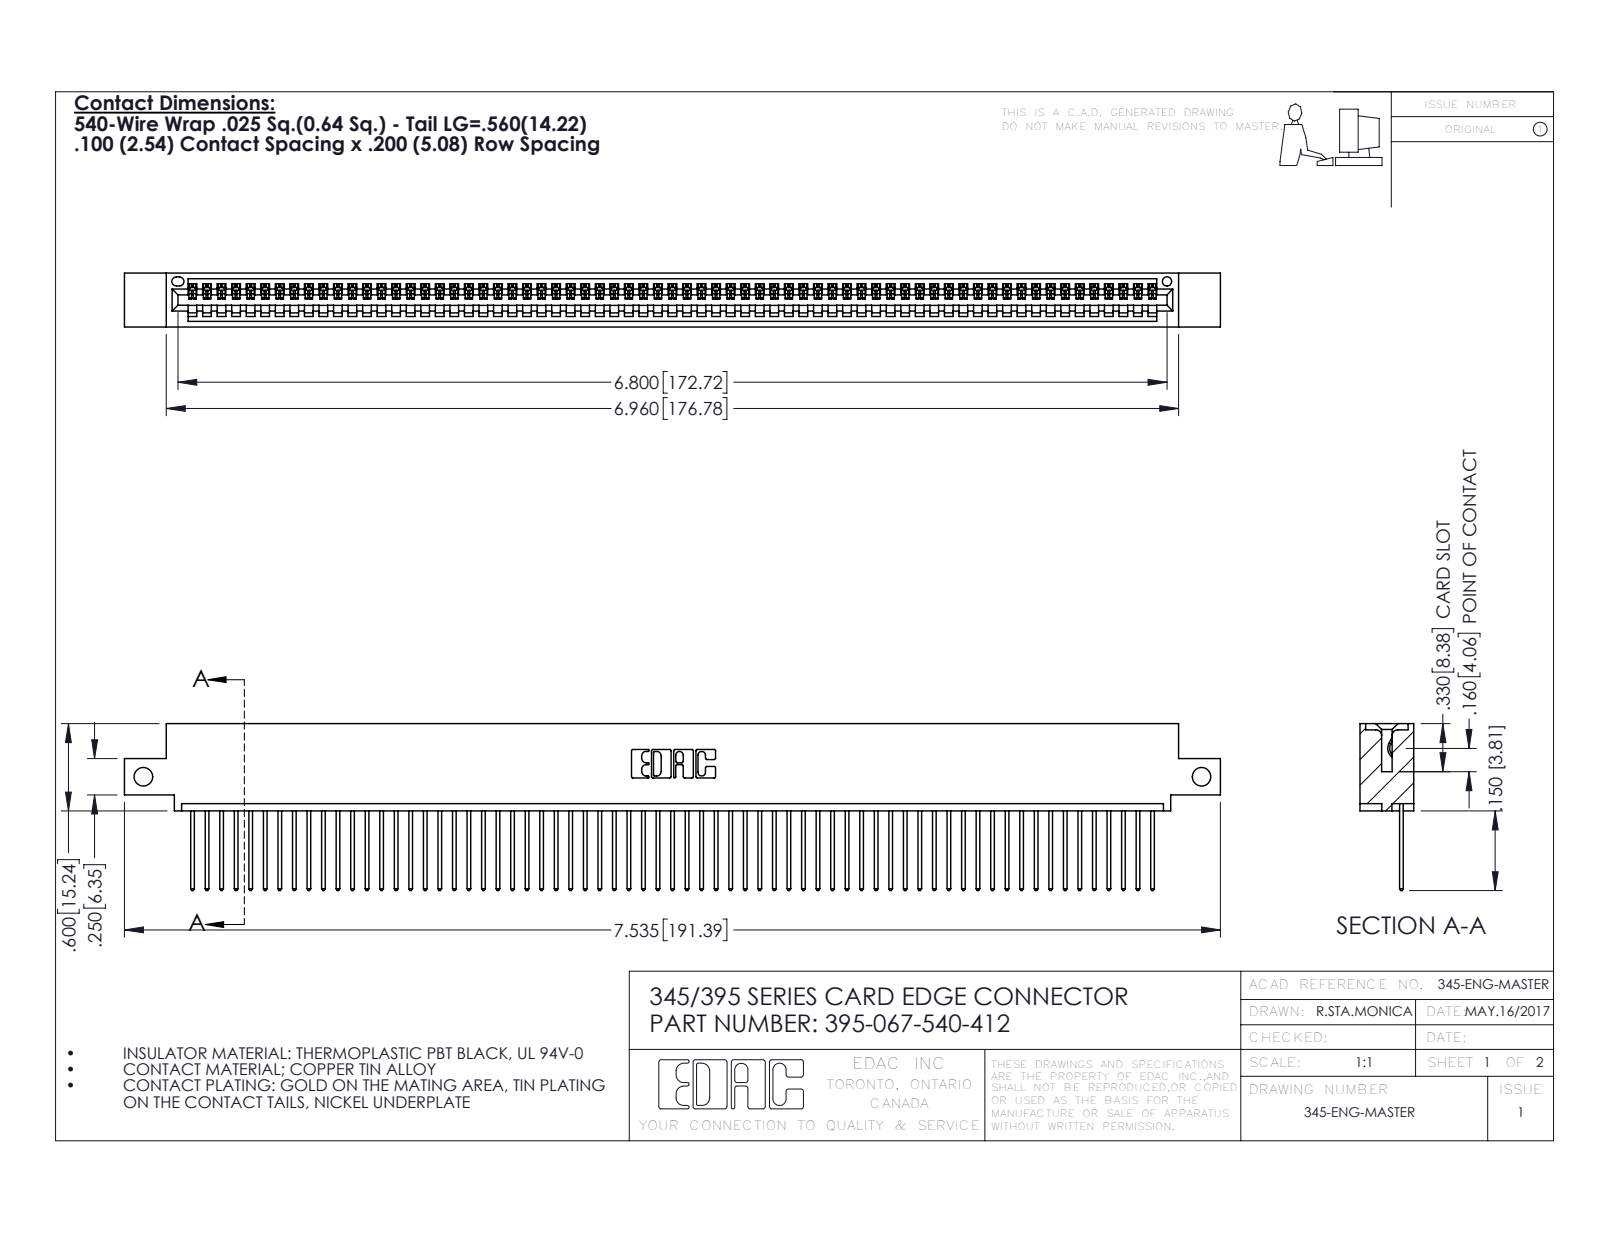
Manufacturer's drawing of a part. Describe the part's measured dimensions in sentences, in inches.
The part is named "395-067-540-412; 345 Part_0.110 Offset - Side Mount; 345-292-001_345-293-140". Its 3-D file was written by "SolidWorks 2016 (CONFIG_CONTROL_DESIGN)". It is 68 solids with 4016 faces: 2764 planar, 1252 cylindrical and 0 other. Overall it measures 7.535 by 1.147 by 0.37 inches. Its volume is 1.118 cubic inches and its surface area 39.17 square inches. Round holes: 2 of diameter 0.128, 1 of diameter 0.064. Partial cylindrical surfaces (rounded edges, fillets, slot ends): 134 of radius 0.006, 134 of radius 0.01, 22 of radius 0.01, 6 of radius 0.007, 6 of radius 0.031, 3 of radius 0.026, 2 of radius 0.031, 2 of radius 0.04. The main face-to-face distances are 0.072, 0.298, 0.37, 0.098, 0.272, 0.025, 0.2, 0.225, 0.149, 0.072. The hole center spacings are 7.275.
